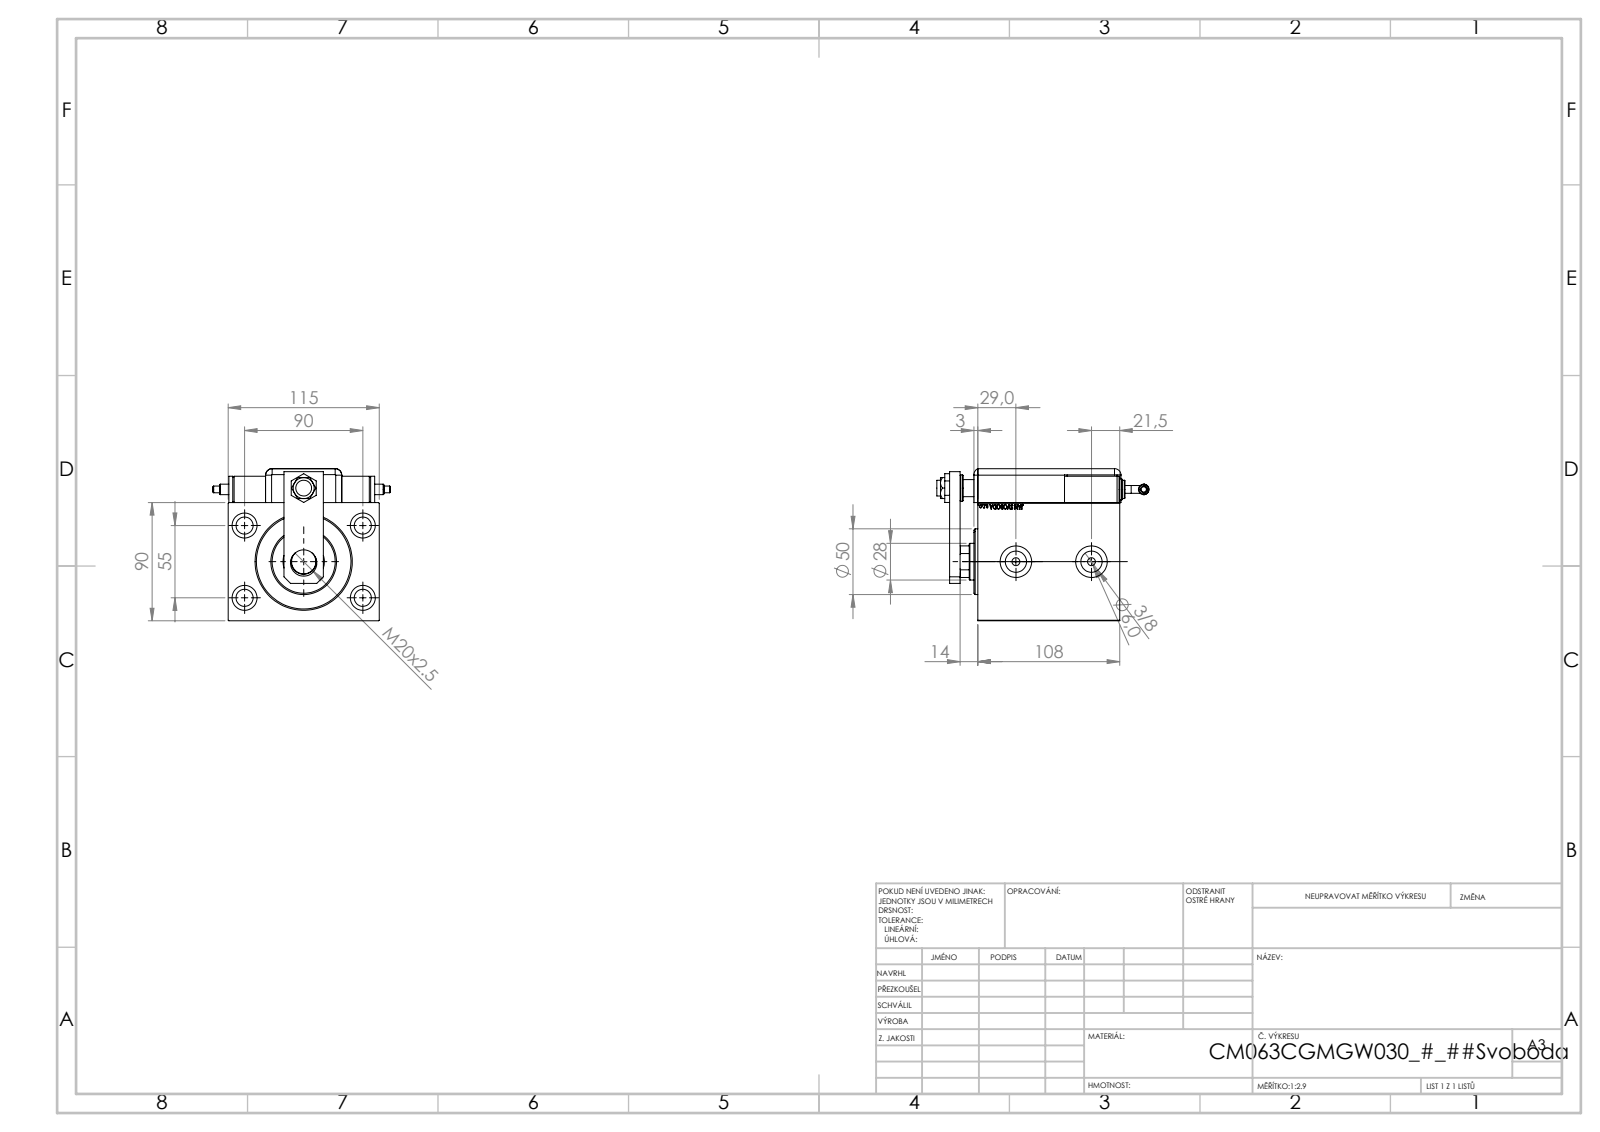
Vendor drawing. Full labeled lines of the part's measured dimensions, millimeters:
Part name (STEP PRODUCT): NUT_D19; TYC; V450CM_VC_B; KRYT (+7 more)
STEP written by: SolidWorks 2019 (CONFIG_CONTROL_DESIGN)
Units: millimetres
Bodies: 13 solids, 1277 faces (619 planar, 125 cylindrical, 533 other)
Overall size (bounding box): 161.46 × 135.01 × 115.8
Volume: 1 117 000 mm³ · Surface area: 195 164 mm²
Round holes (diameter × count): ⌀13 ×5, ⌀19 ×4, ⌀4 ×2, ⌀6 ×2, ⌀8 ×2, ⌀16.17 ×2, ⌀24 ×2, ⌀12 ×1, ⌀14 ×1, ⌀18.5 ×1, ⌀20 ×1, ⌀28 ×1
Round bosses / shafts (diameter × count): ⌀20 ×3, ⌀16 ×2, ⌀14 ×2, ⌀8 ×2, ⌀6 ×2, ⌀5.04 ×2, ⌀50 ×1
Partial cylindrical surfaces — rounded edges, fillets, slot ends (radius × count): R5 ×9, R10 ×1, R13.5 ×1
Main face-to-face distances: 90, 3, 108, 115, 90.5, 17.5, 13.5, 8, 25.8, 115.8
Hole centre spacings: 52.74, 53.27, 52.22, 55, 90, 94.85, 105.48, 1
